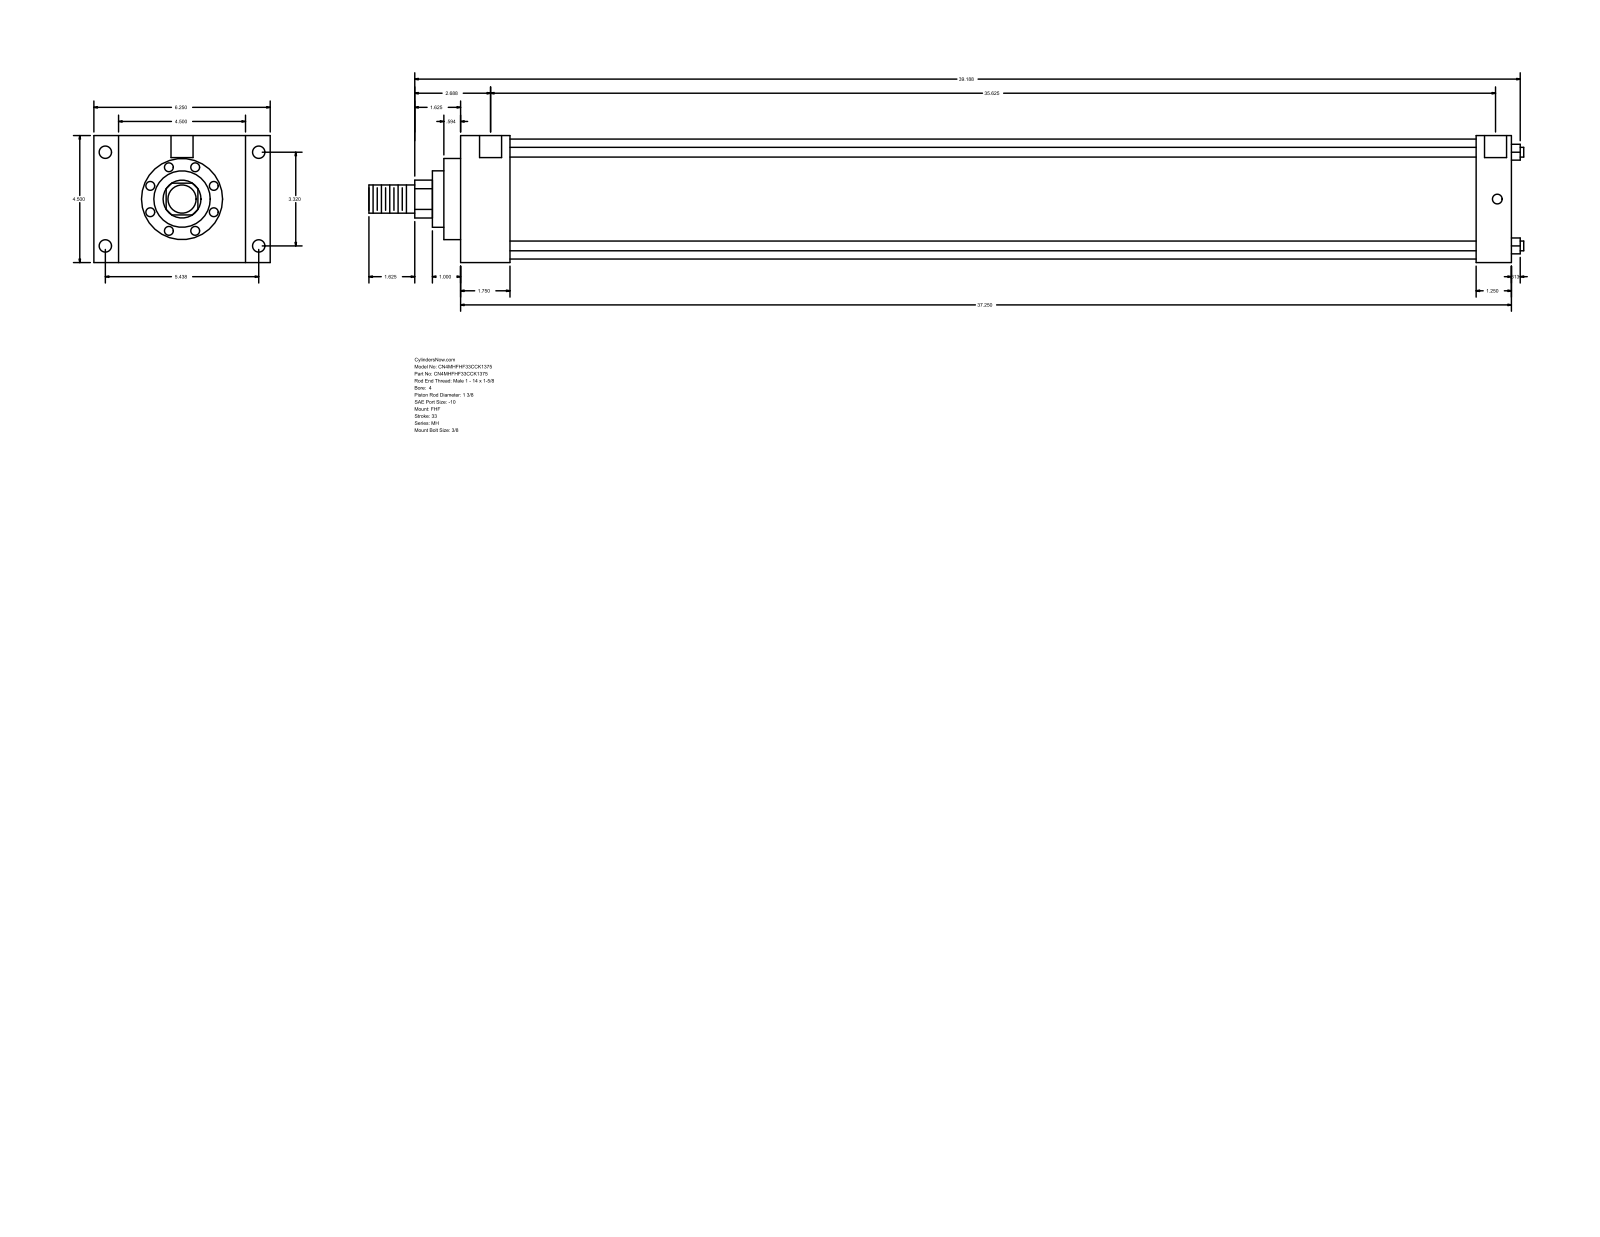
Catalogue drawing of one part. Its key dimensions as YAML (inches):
part_name: "MH_FHF__0400_1.375"
step_written_by: "GSSL Pune (CONFIG_CONTROL_DESIGN)"
units: inches
bodies: {solids: 0, faces: 90, planar: 61, cylindrical: 29, other: 0}
overall_size: [40.937, 6.25, 4.5]
round_holes:
  - {diameter: 0.344, count: 4}
  - {diameter: 0.438, count: 4}
  - {diameter: 0.781, count: 2}
round_bosses_or_shafts:
  - {diameter: 0.345, count: 4}
  - {diameter: 4.25, count: 1}
  - {diameter: 2.875, count: 1}
  - {diameter: 2, count: 1}
  - {diameter: 1.375, count: 1}
  - {diameter: 1, count: 1}
partial_cylinders:
  - {radius: 0.672, count: 1}
face_to_face_distances: [4.5, 37.25, 1.75, 35.5, 0.875, 5.375, 6.25, 36, 34.25, 1.25]
hole_center_spacings: [0.063, 3.32, 5.438, 6.371, 35.688, 35.75, 35.625]
